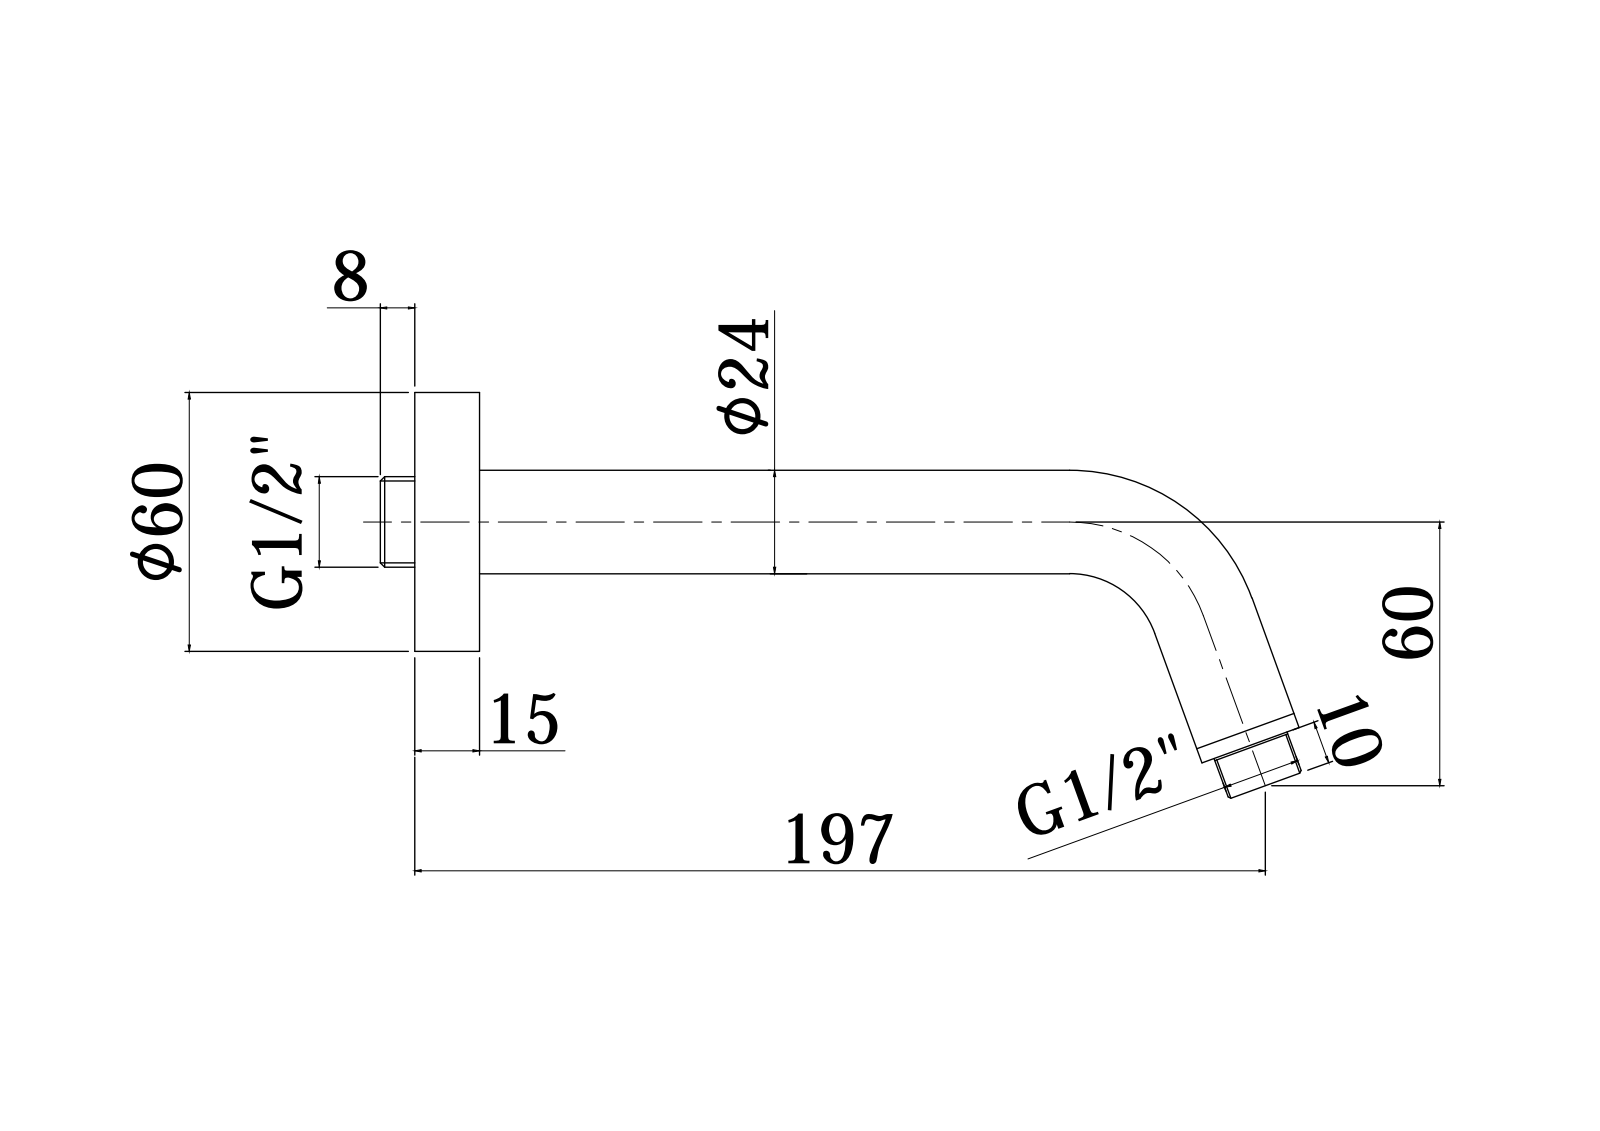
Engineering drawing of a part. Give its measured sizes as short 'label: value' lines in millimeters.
name: ZSOF038CR
written by: CREO PARAMETRIC BY PTC INC, 2020044 (CONFIG_CONTROL_DESIGN)
unit: mm
bodies: 1 solid, 49 faces (13 planar, 26 cylindrical, 10 other)
size: 221.12 × 95.47 × 60
volume: 119 396 mm³; area: 30 081 mm²
holes: 1× ⌀24.5, 1× ⌀26, 1× ⌀56.4
bosses: 2× ⌀24, 2× ⌀21, 1× ⌀60, 1× ⌀28, 1× ⌀18.6, 1× ⌀18.5
face distances: 2.5, 15, 17, 12.5, 2, 29.5, 32, 10, 14.5, 26.5
